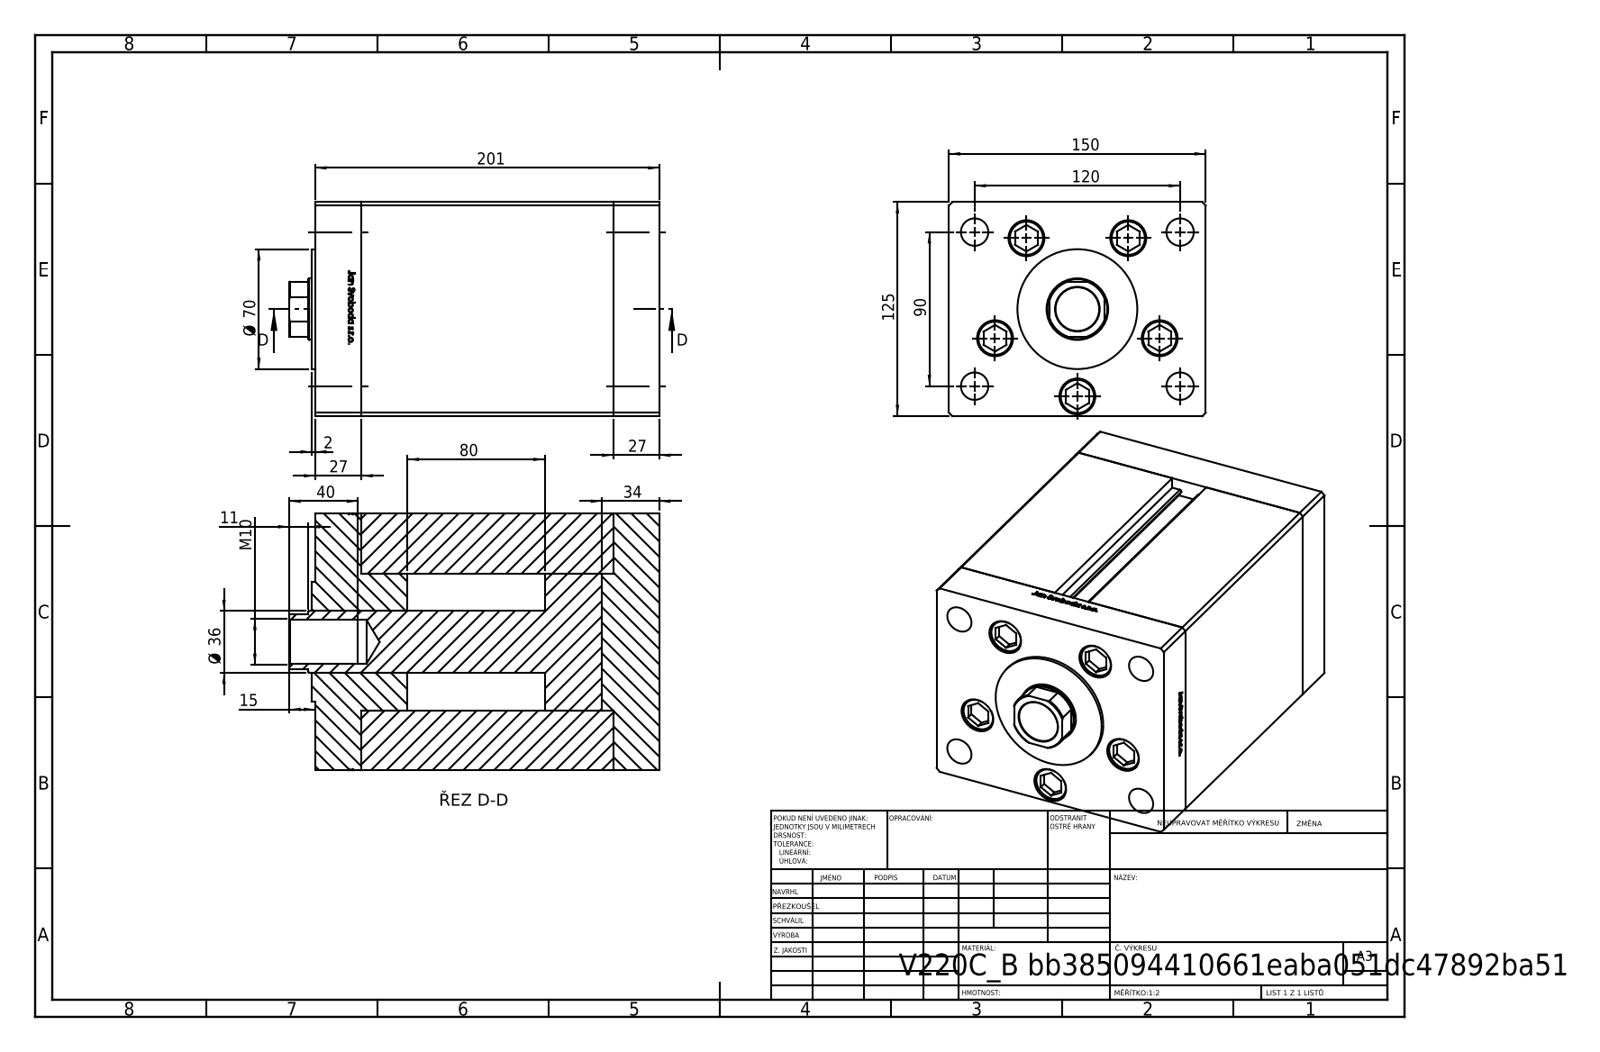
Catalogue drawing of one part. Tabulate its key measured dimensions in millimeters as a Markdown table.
| quantity | value |
| --- | --- |
| part name | V220C BACK_B; ALLEN BOLT; V220C_VC_B; V220C_B MIDDLE (+1 more) |
| STEP written by | SolidWorks 2019 (CONFIG_CONTROL_DESIGN) |
| units | millimeters |
| bodies | 14 solids, 1185 faces (464 planar, 147 cylindrical, 574 other) |
| overall size | 216 × 150 × 125 |
| volume | 3 289 000 mm³ |
| surface area | 349 130 mm² |
| round holes (diameter × count) | 17.5 × 5, 21 × 5, 16 × 4, 2 × 2, 13.16 × 2, 25.5 × 1, 36 × 1 |
| round bosses / shafts (diameter × count) | 8 × 5, 80 × 1, 70 × 1 |
| partial cylindrical surfaces (radius × count) | 0.93 × 2, 17.5 × 1 |
| main face-to-face distances | 27, 174, 147, 125, 150, 33.5, 201, 6.5, 140.5, 167.5 |
| hole center spacings | 51, 75, 30.43, 30.48, 58.89, 60.3, 61.25, 63.14 |
